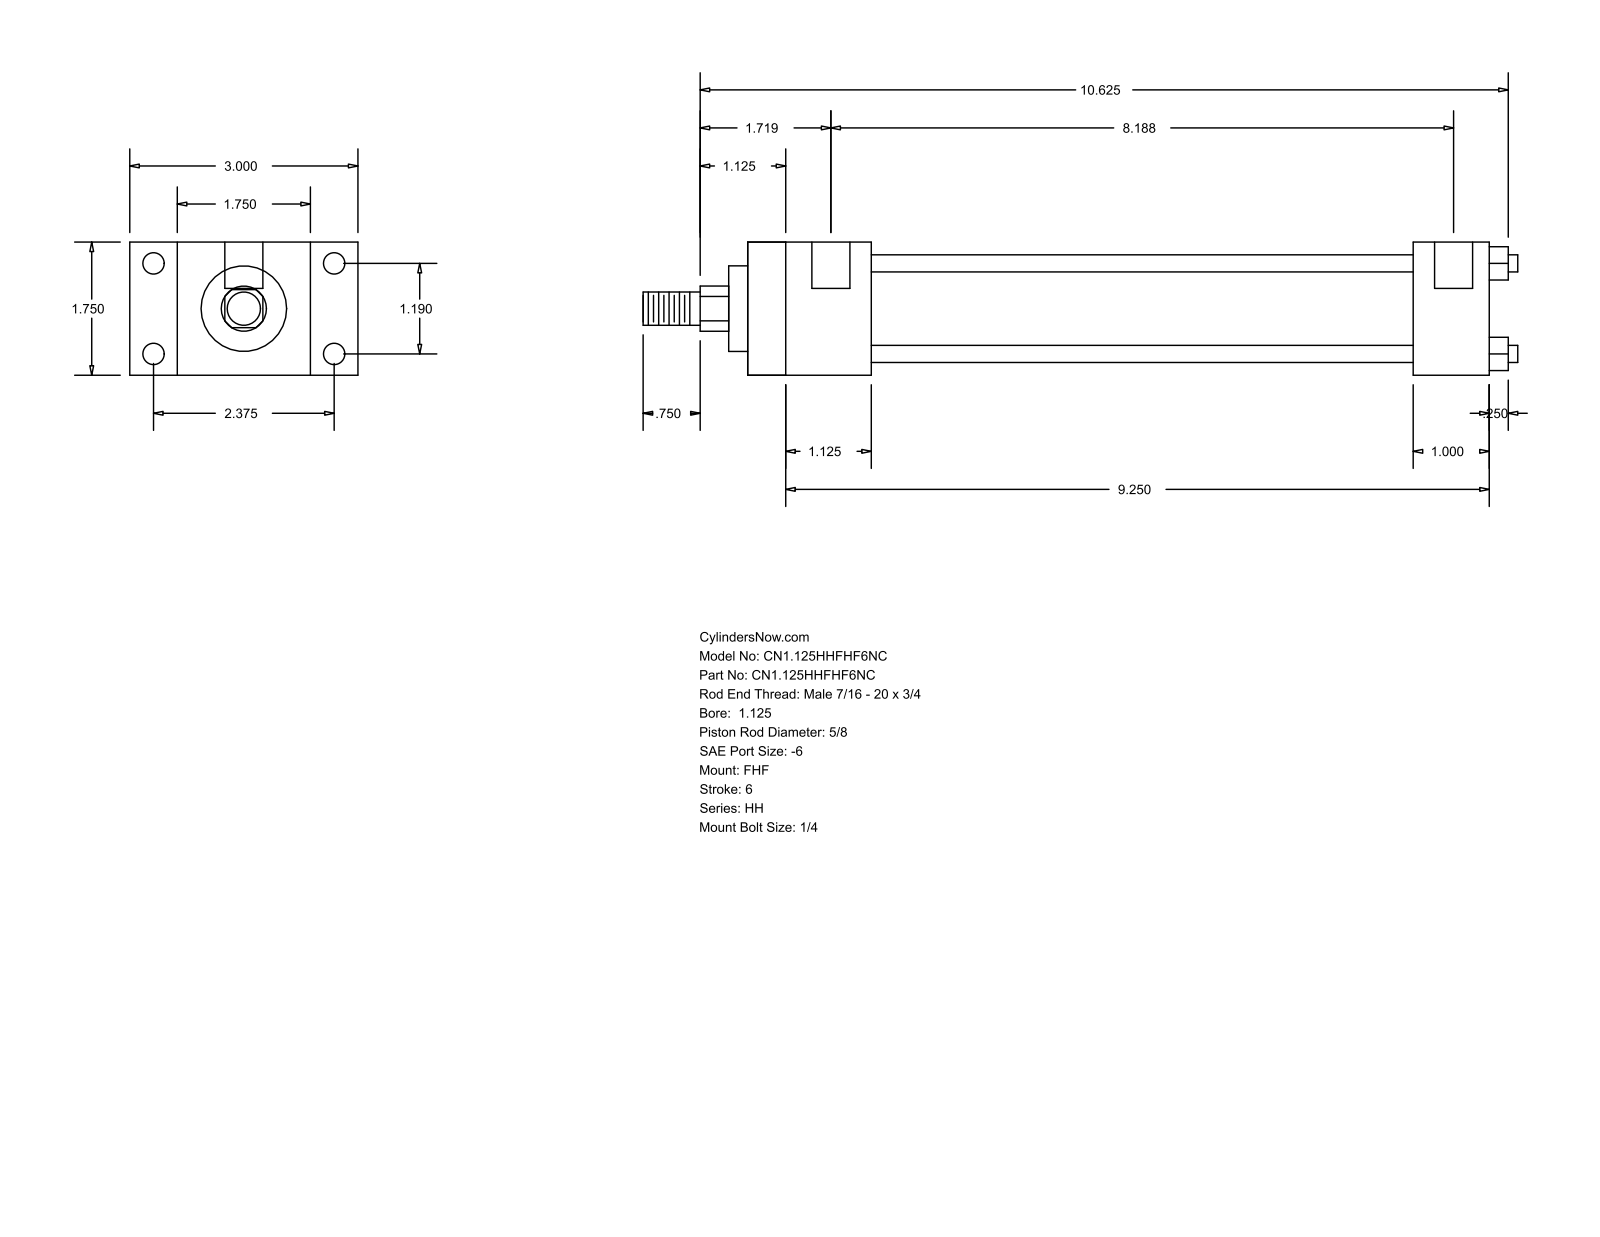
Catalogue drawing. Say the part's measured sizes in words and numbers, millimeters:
The part is named "HH_FHF__0112_0.625". Its 3-D file was written by "GSSL Pune (CONFIG_CONTROL_DESIGN)". It is 0 solids with 88 faces: 60 planar, 28 cylindrical and 0 other. Overall it measures 292.1 by 76.2 by 44.45 millimeters. Round holes: 4 of diameter 5.56, 4 of diameter 7.14, 2 of diameter 12.7. Round bosses or shafts: 4 of diameter 5.71, 1 of diameter 34.92, 1 of diameter 28.57, 1 of diameter 15.88, 1 of diameter 11.11. Partial cylindrical surfaces (rounded edges, fillets, slot ends): 1 of radius 7.54. The main face-to-face distances are 44.46, 15.87, 60.33, 41.27, 76.2, 247.64, 206.37, 25.4, 222.24, 180.97. The hole center spacings are 30.22, 60.32, 67.47, 204.79, 3.17, 207.96.
